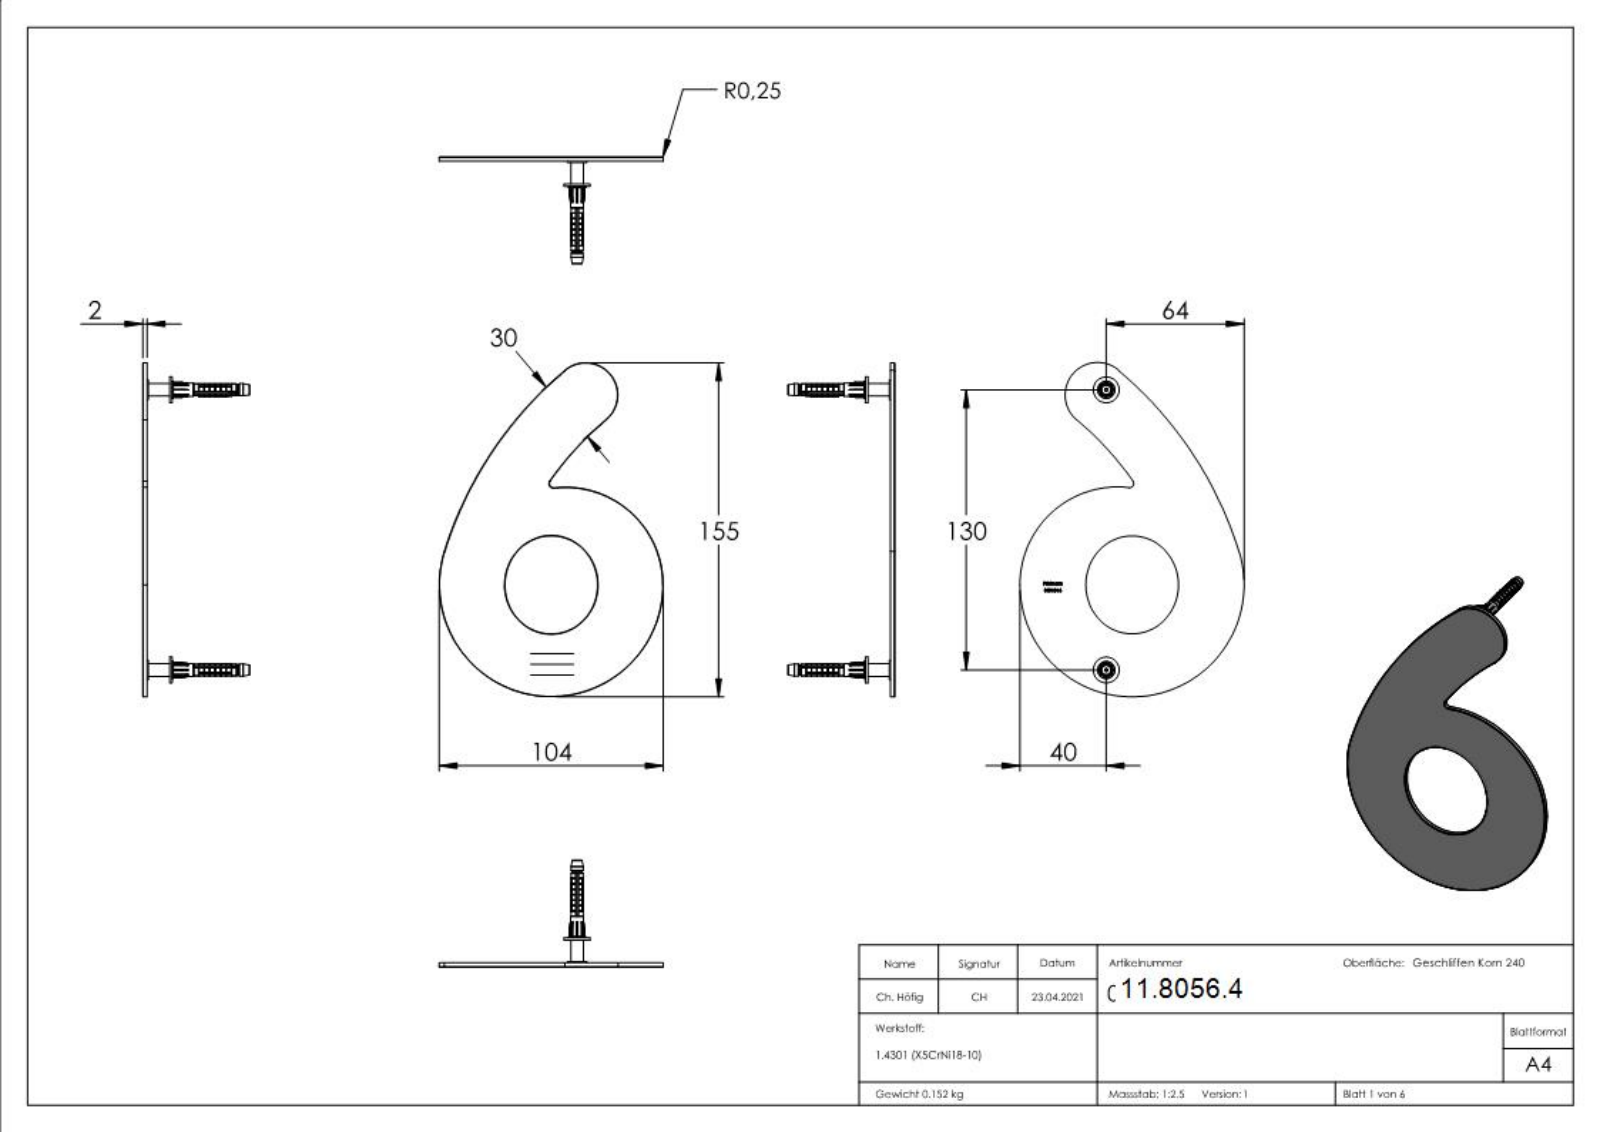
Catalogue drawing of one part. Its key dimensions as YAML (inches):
part_name: "040-HN-X Teil3; 040-HN-X Teil4; 040-HN-X Teil1_040-HN-6 Teil1; 040-HN-X Teil2 (+5 more)"
step_written_by: "SolidWorks 2018 (CONFIG_CONTROL_DESIGN)"
units: inches
bodies: {solids: 7, faces: 1554, planar: 355, cylindrical: 386, other: 813}
overall_size: [393.701, 205.411, 181.413]
volume: 1.234
surface_area: 35.75
round_holes:
  - {diameter: 0.13, count: 2}
  - {diameter: 0.169, count: 2}
round_bosses_or_shafts:
  - {diameter: 0.472, count: 2}
  - {diameter: 0.354, count: 2}
  - {diameter: 0.315, count: 2}
  - {diameter: 0.236, count: 2}
  - {diameter: 0.228, count: 2}
  - {diameter: 0.22, count: 2}
  - {diameter: 0.181, count: 2}
  - {diameter: 0.157, count: 2}
partial_cylinders:
  - {radius: 0.004, count: 22}
  - {radius: 0.138, count: 2}
  - {radius: 0.079, count: 1}
  - {radius: 0.591, count: 1}
  - {radius: 1.784, count: 1}
  - {radius: 2.047, count: 1}
  - {radius: 5.906, count: 1}
  - {radius: 7.087, count: 1}
face_to_face_distances: [0.079, 0.457, 0.535, 0.043, 0.413, 0.492, 0.02, 0.098, 0.394, 0.437]
hole_center_spacings: [5.118]
